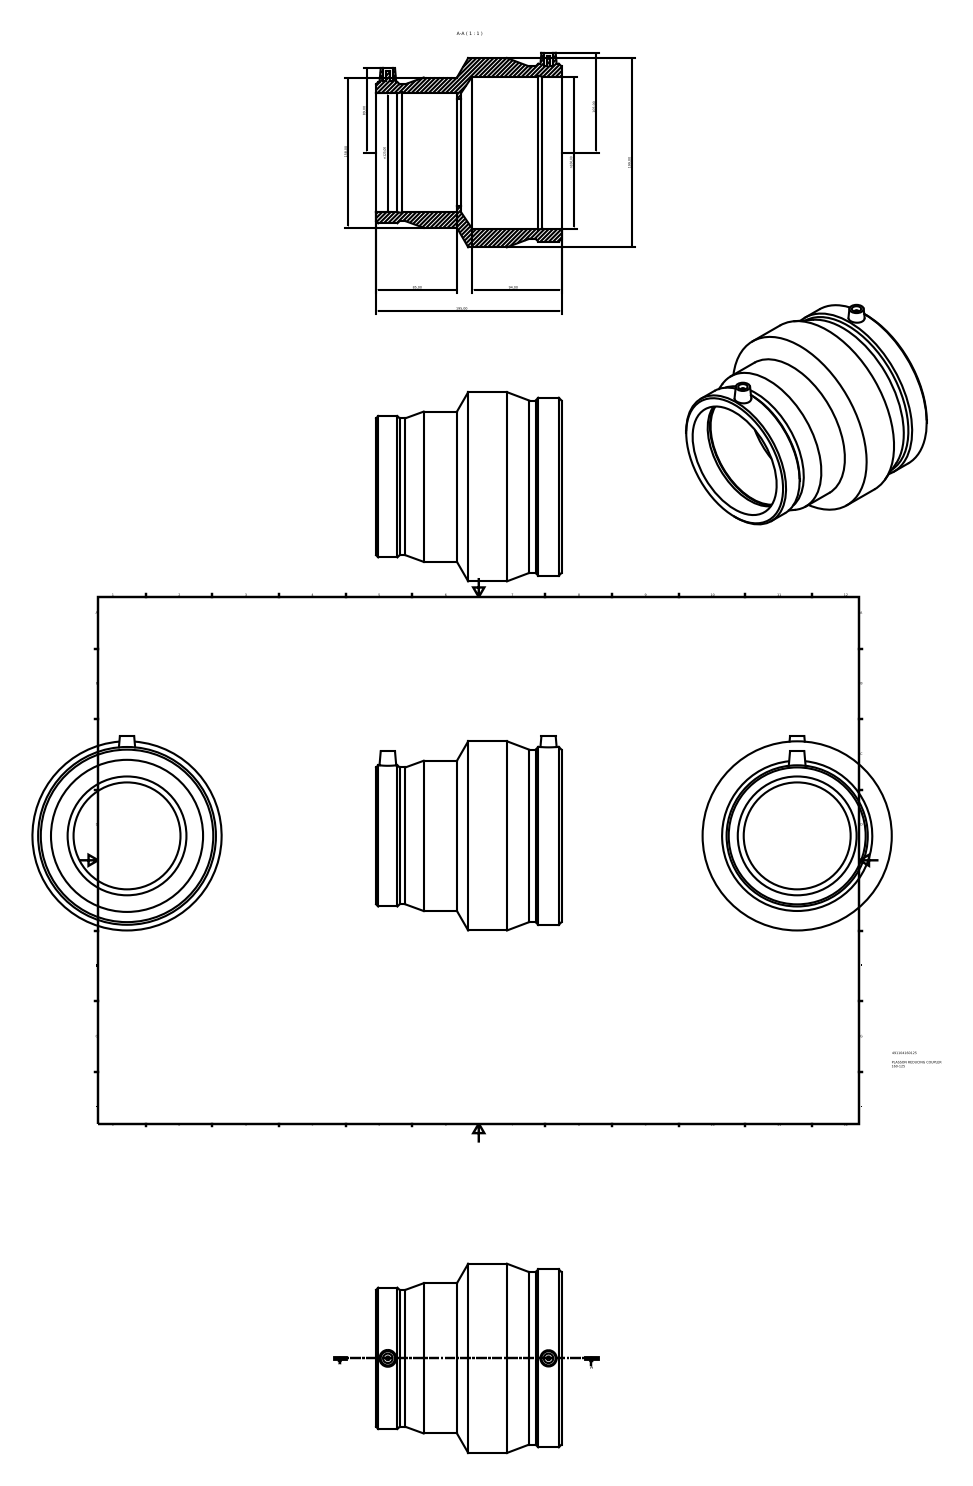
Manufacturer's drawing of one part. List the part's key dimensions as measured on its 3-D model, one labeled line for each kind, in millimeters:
Part name (STEP PRODUCT): 491104160125
STEP written by: Autodesk Inventor 2015 (AUTOMOTIVE_DESIGN)
Units: millimetres
Bodies: 1 solid, 39 faces (12 planar, 15 cylindrical, 12 other)
Overall size (bounding box): 204.5 × 199 × 195
Volume: 1 543 000 mm³ · Surface area: 226 359 mm²
Round holes (diameter × count): ⌀10 ×2, ⌀112.5 ×1, ⌀125 ×1, ⌀160 ×1
Round bosses / shafts (diameter × count): ⌀4 ×2, ⌀199 ×1, ⌀187.06 ×1, ⌀181.45 ×1, ⌀158 ×1, ⌀148.52 ×1, ⌀144.06 ×1
Main face-to-face distances: 195, 89.25, 105.75, 85, 4.25, 110, 170.55, 85.55, 81.3, 24.45
Hole centre spacings: 169.04
